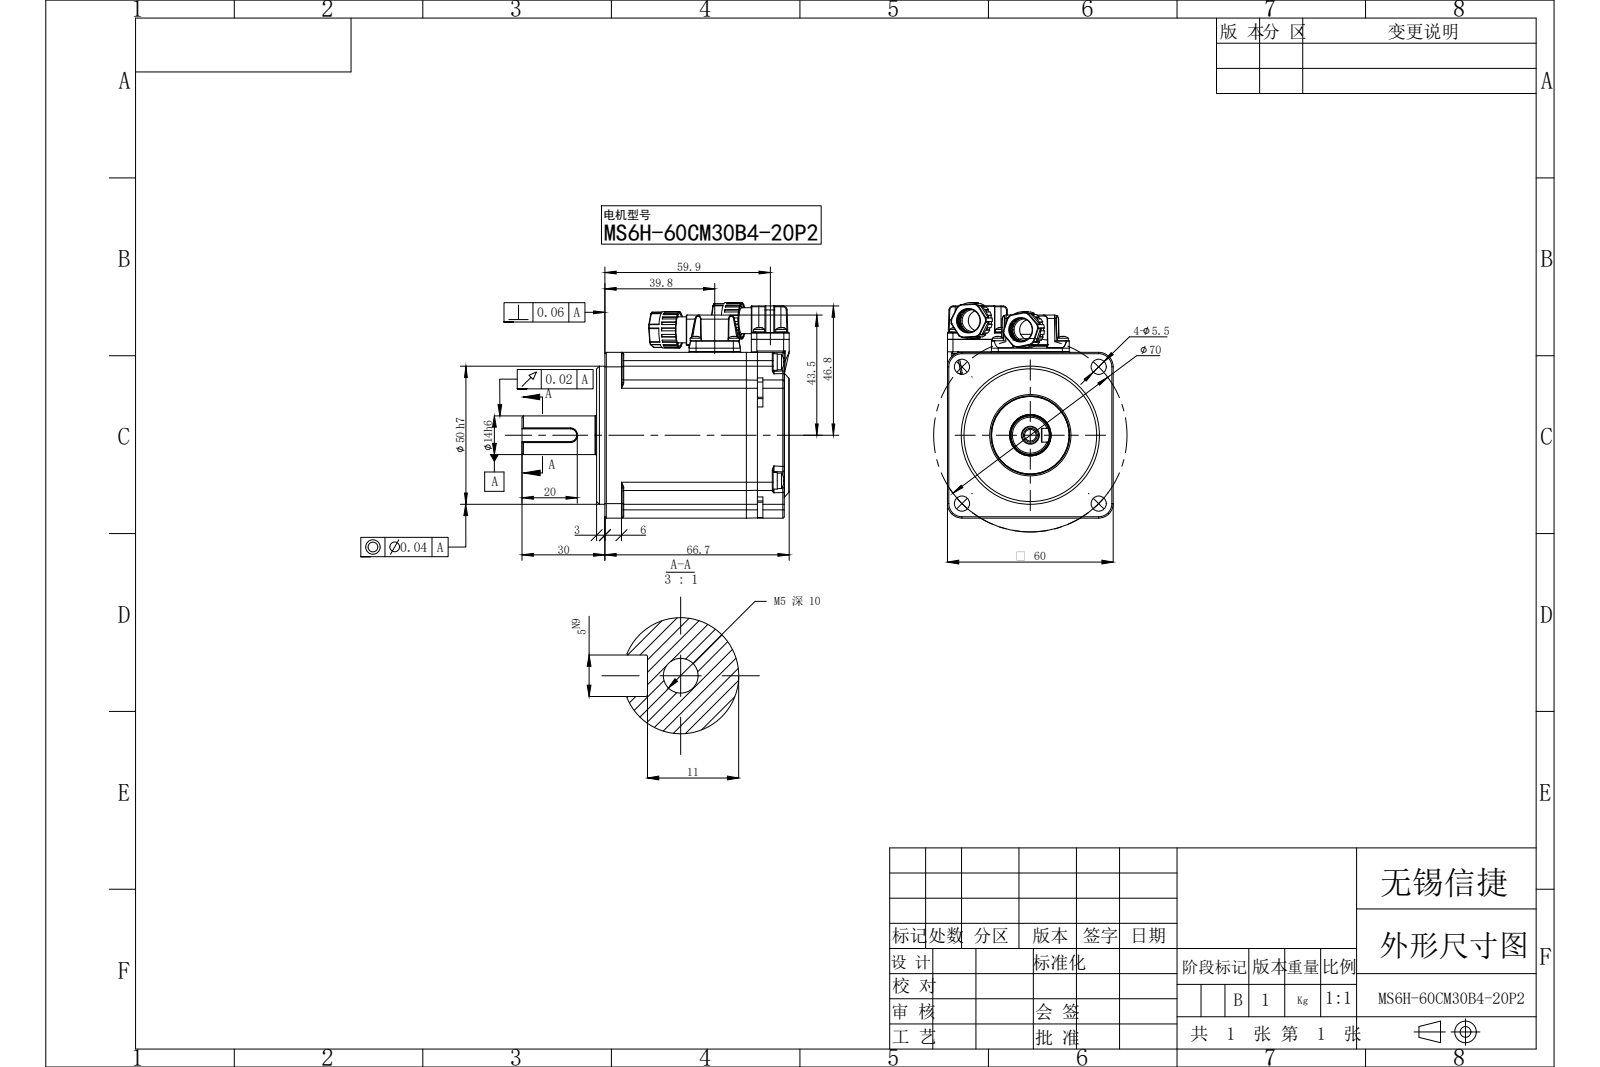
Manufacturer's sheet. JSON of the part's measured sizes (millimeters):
{"part_name": "MS6H-60CM30B4-20P2", "step_written_by": "SolidWorks 2022 (CONFIG_CONTROL_DESIGN)", "units": "millimeters", "bodies": {"solids": 0, "faces": 1208, "planar": 491, "cylindrical": 423, "other": 294}, "overall_size": [96.7, 78.06, 60], "round_holes": [[5.5, 4], [11.5, 2], [11.7, 2], [4.2, 1], [5, 1], [10.4, 1], [15, 1]], "round_bosses_or_shafts": [[4, 8], [6, 4], [5.6, 4], [5.5, 4], [9.4, 2], [50, 1], [28, 1], [14.8, 1]], "partial_cylinders_radius": [[0.5, 50], [0.3, 42], [0.35, 25], [0.2, 19], [3, 17], [1.5, 13], [0.15, 10], [2, 10]], "face_to_face_distances": [60, 1.8, 66.7, 11.5, 55.2, 9.7, 4, 64.9, 13.7, 54.2], "hole_center_spacings": [35, 49.5, 23.56, 23.57, 70, 23.55]}
